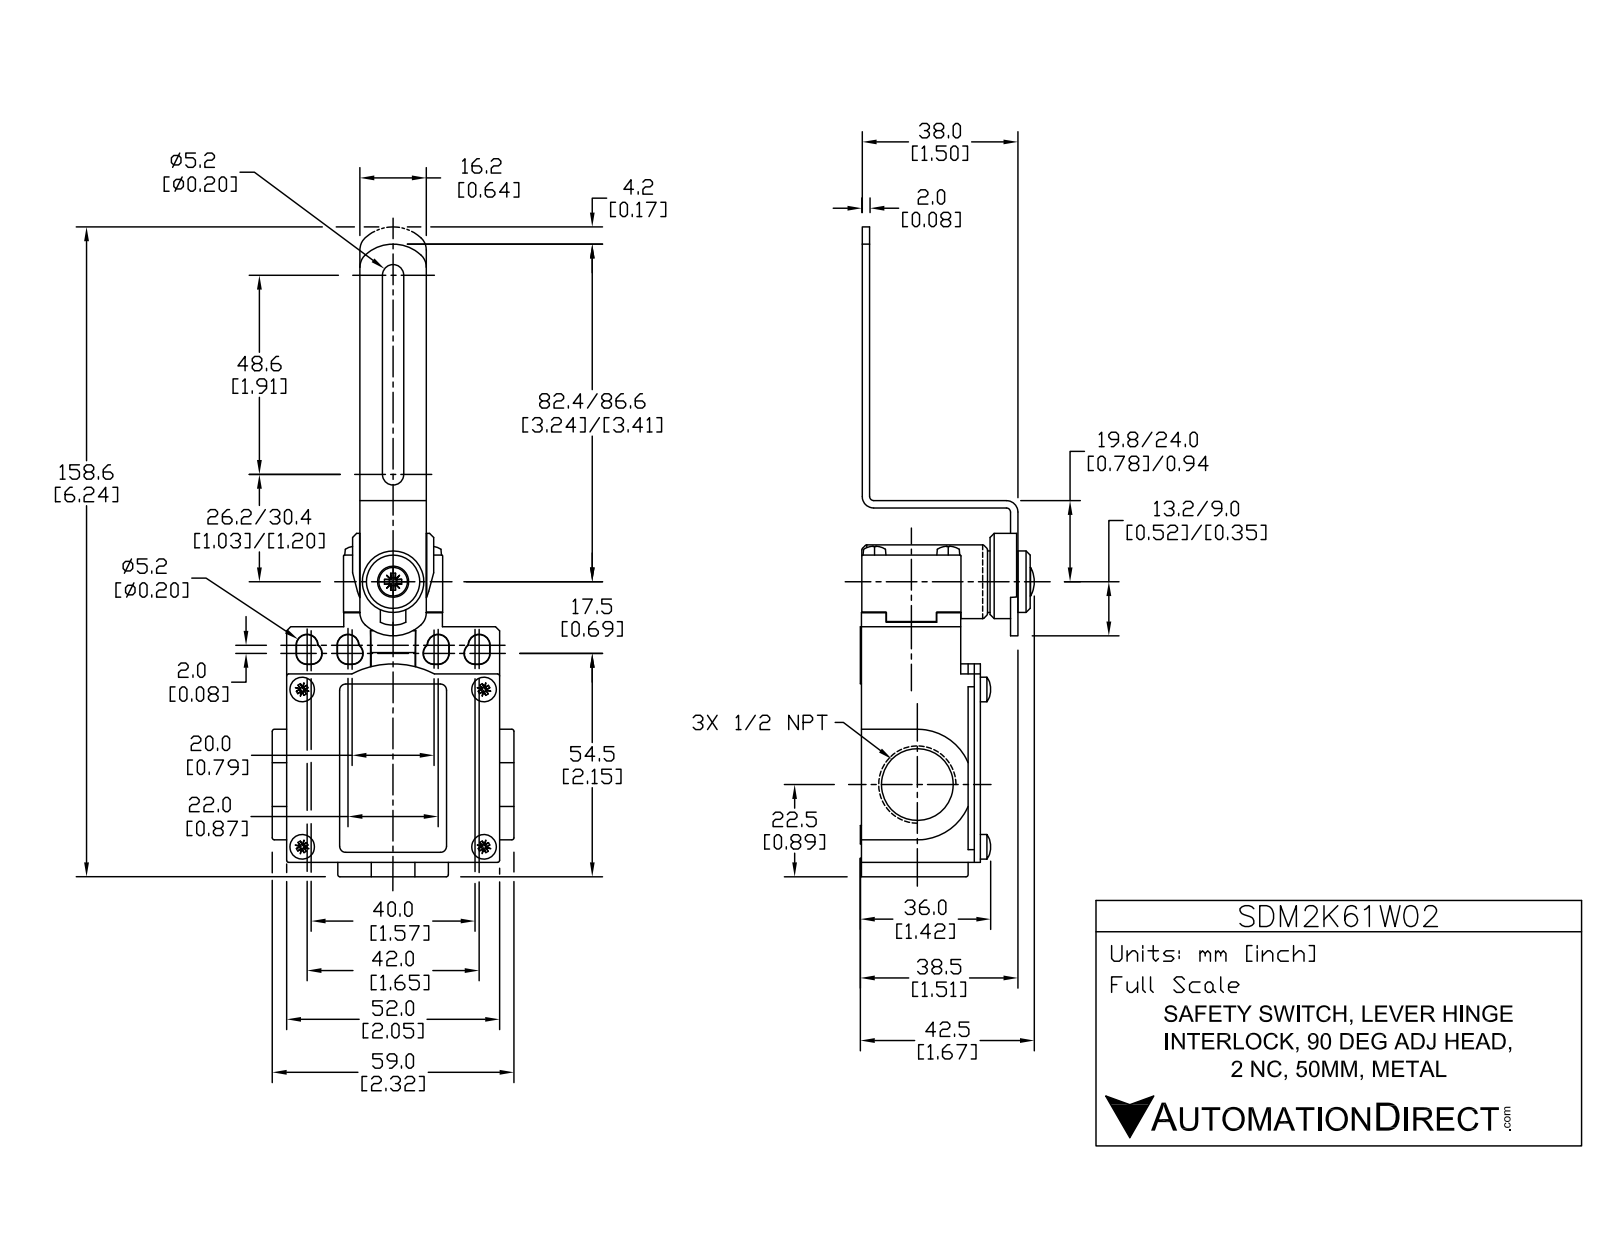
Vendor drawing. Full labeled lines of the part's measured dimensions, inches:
Part name (STEP PRODUCT): SDM2K61W02
STEP written by: SolidWorks 2017 (AUTOMOTIVE_DESIGN)
Units: inches
Bodies: 5 solids, 293 faces (152 planar, 107 cylindrical, 34 other)
Overall size (bounding box): 6.161 × 2.323 × 1.656
Volume: 6.167 in³ · Surface area: 39.86 in²
Round holes (diameter × count): ⌀0.669 ×2, ⌀0.748 ×2, ⌀0.299 ×1, ⌀0.433 ×1
Round bosses / shafts (diameter × count): ⌀0.22 ×4, ⌀0.217 ×4, ⌀0.709 ×1, ⌀0.591 ×1, ⌀0.276 ×1
Partial cylindrical surfaces — rounded edges, fillets, slot ends (radius × count): R0.02 ×14, R0.102 ×14, R0.157 ×4, R0.394 ×3, R0.039 ×2, R0.11 ×2, R0.283 ×2, R0.531 ×2
Main face-to-face distances: 1.144, 0.071, 1.496, 0.138, 1.425, 2.047, 0.945, 0.551, 0.689, 2.307
